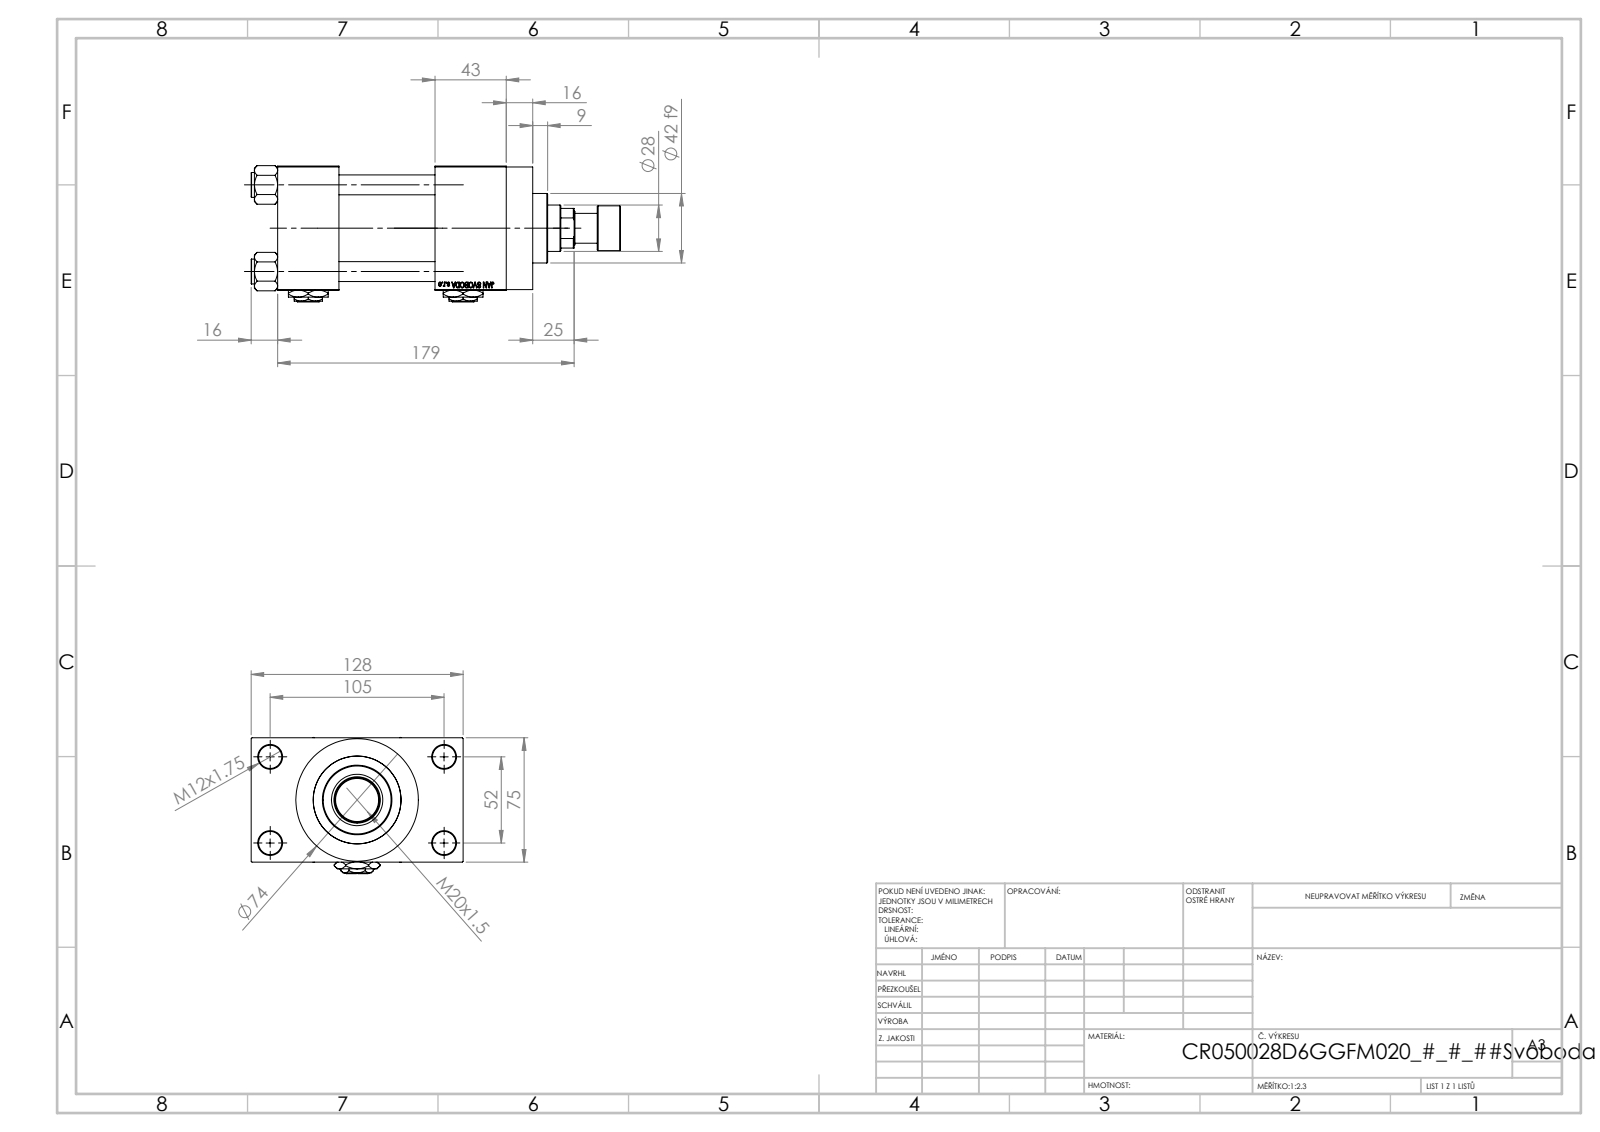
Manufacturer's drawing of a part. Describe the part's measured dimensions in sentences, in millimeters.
The part is named "V215CR_D_TYCINKA; V215_VC_A; V215CR_D_Body; NUT_M5_D (+3 more)". Its 3-D file was written by "SolidWorks 2019 (CONFIG_CONTROL_DESIGN)". It is 14 solids with 1219 faces: 549 planar, 104 cylindrical and 566 other. Overall it measures 223 by 128 by 82.27 millimeters. Its volume is 822 476 cubic millimeters and its surface area 176 361 square millimeters. Round holes: 4 of diameter 12, 4 of diameter 14, 2 of diameter 7, 2 of diameter 20.96, 2 of diameter 30, 1 of diameter 18.5, 1 of diameter 28, 1 of diameter 31, 1 of diameter 41, 1 of diameter 50, 1 of diameter 53. Round bosses or shafts: 4 of diameter 15, 1 of diameter 74, 1 of diameter 56, 1 of diameter 42, 1 of diameter 27, 1 of diameter 18. The main face-to-face distances are 75, 58, 37, 95, 101.5, 26.5, 138, 101, 43, 16. The hole center spacings are 26.35, 36.98, 52.3, 58.43, 58.59, 78.65, 94.37, 52.
